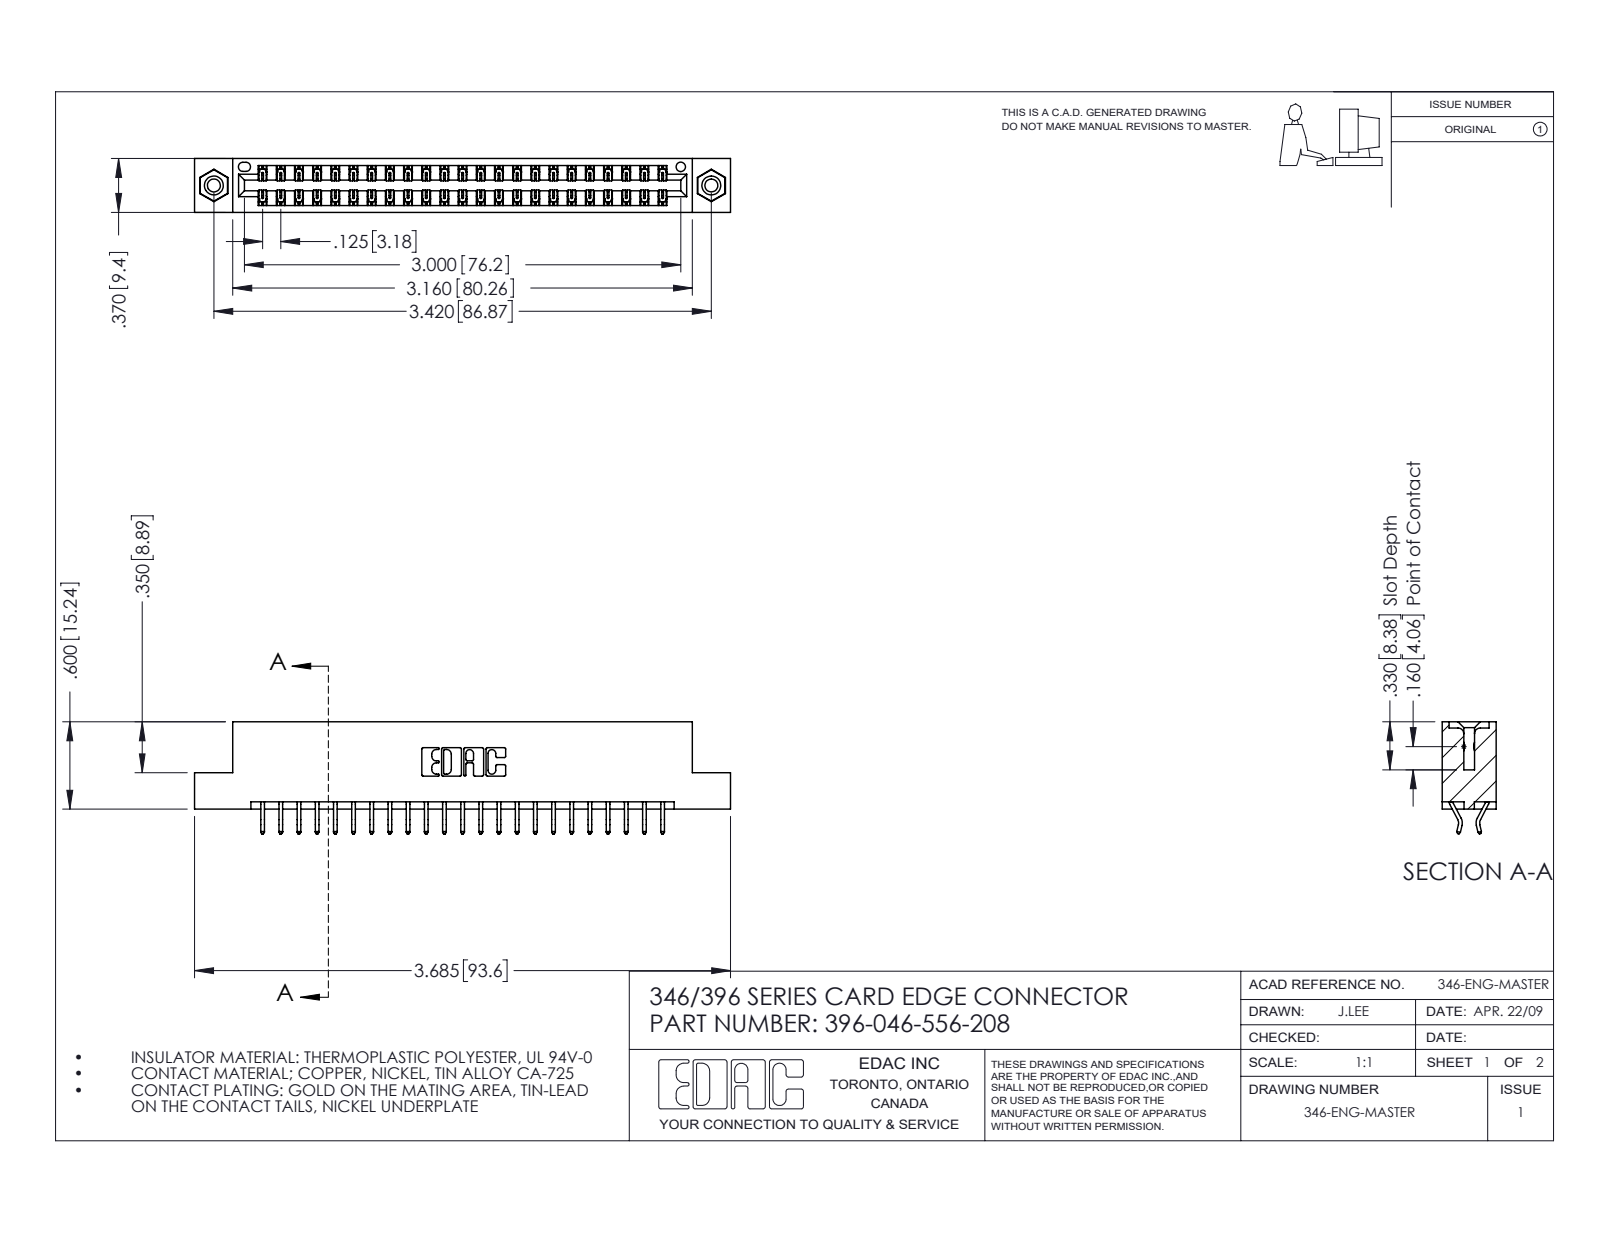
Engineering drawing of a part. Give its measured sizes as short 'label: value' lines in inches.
name: 396-046-556-208; 345-250-001_345-250-003-102; 345-292-001_556 Tail; 346 Part_Flush Mounting Lugs - 0.156 Dia-TI
written by: SolidWorks 2016 (CONFIG_CONTROL_DESIGN)
unit: in
bodies: 49 solids, 2850 faces (1902 planar, 932 cylindrical, 16 other)
size: 3.685 × 0.77 × 0.37
volume: 0.547 in³; area: 18.62 in²
holes: 2× ⌀0.089, 2× ⌀0.125, 2× ⌀0.156, 1× ⌀0.064
bosses: 2× ⌀0.155
rounds: 69× R0.006, 22× R0.01, 6× R0.007, 6× R0.031, 3× R0.026, 2× R0.01, 2× R0.014, 2× R0.022
face distances: 0.048, 0.322, 0.25, 0.37, 0.025, 0.072, 0.298, 0.275, 0.148, 0.222
hole spacings: 0.246, 3.212, 3.42
